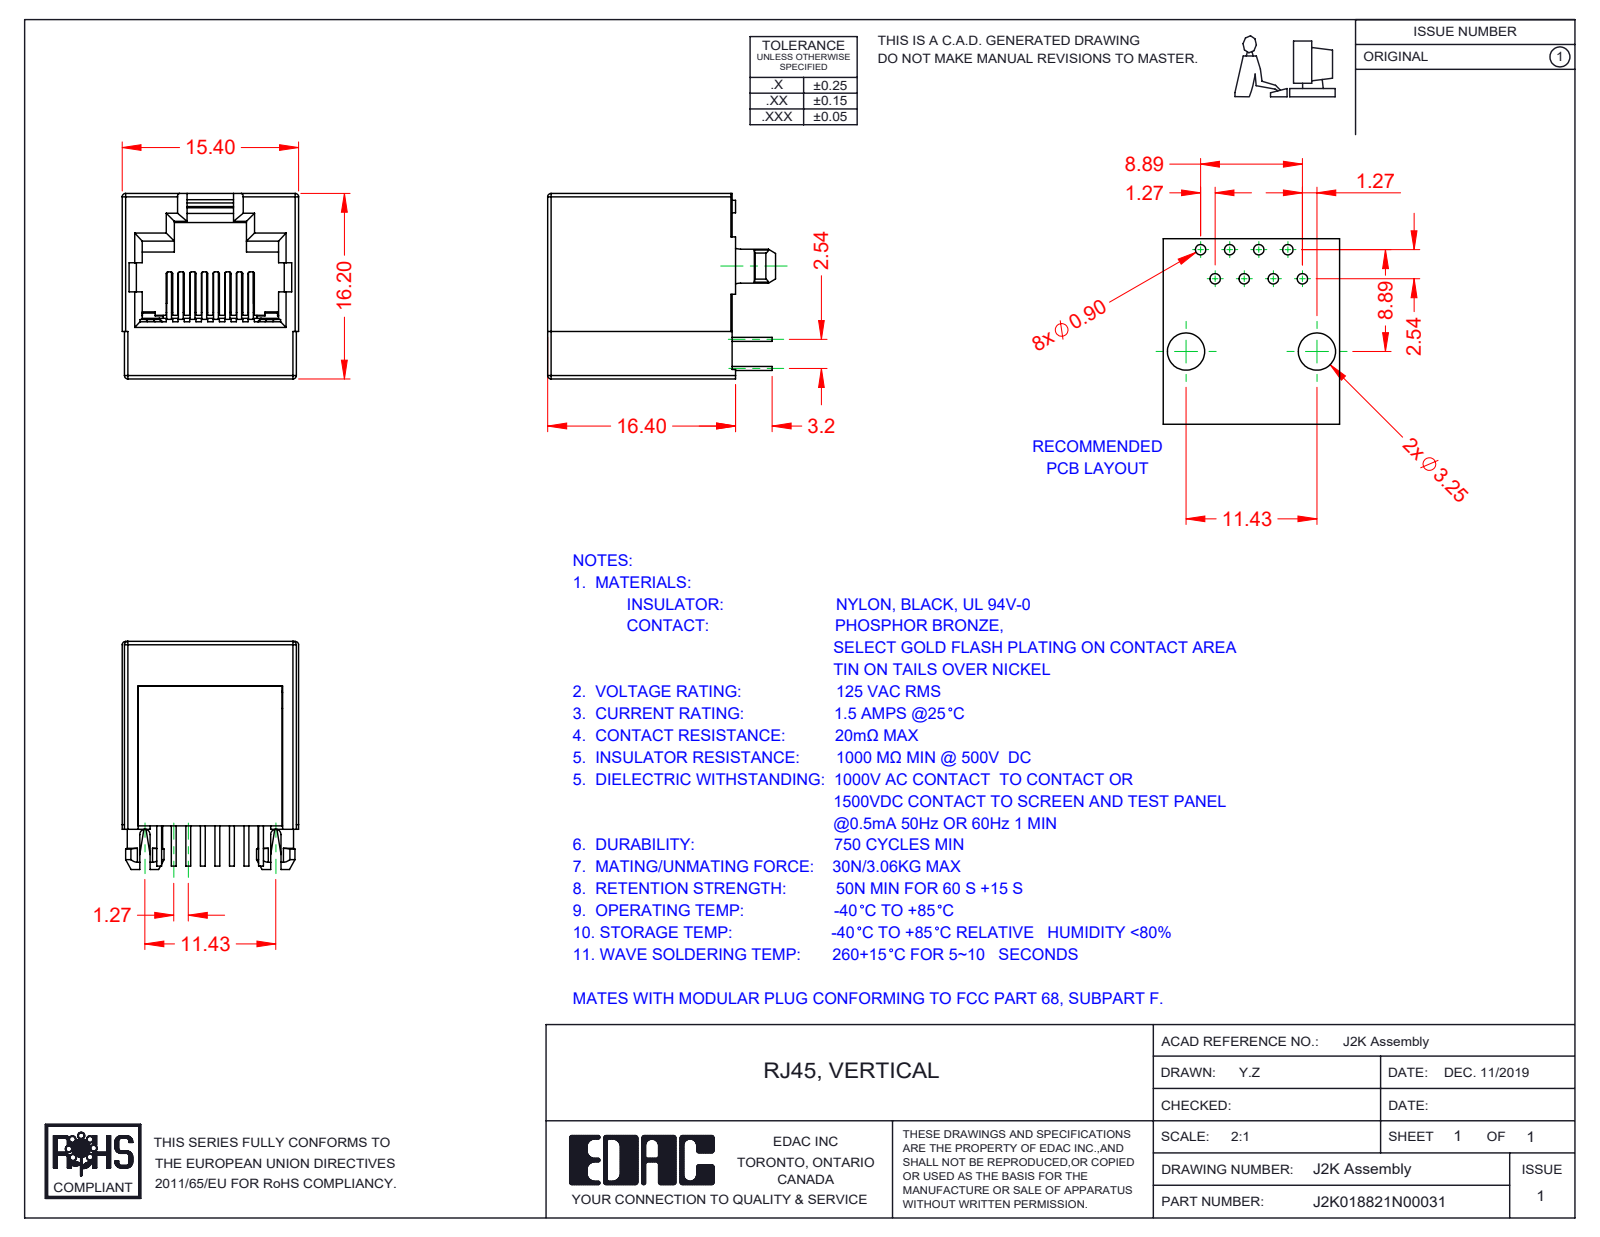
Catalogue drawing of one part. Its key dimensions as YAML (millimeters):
part_name: "2K Insulator; 2K Contact Lock; 2K Contacts; RJ2K018821N00031"
step_written_by: "SolidWorks 2016 (CONFIG_CONTROL_DESIGN)"
units: millimeters
bodies: {solids: 10, faces: 723, planar: 586, cylindrical: 113, other: 24}
overall_size: [19.9, 16.2, 15.4]
volume: 2473
surface_area: 3962
round_bosses_or_shafts:
  - {diameter: 3.1, count: 2}
  - {diameter: 1.1, count: 2}
partial_cylinders:
  - {radius: 0.15, count: 16}
  - {radius: 0.3, count: 10}
  - {radius: 0.5, count: 3}
  - {radius: 0.1, count: 2}
  - {radius: 0.2, count: 2}
  - {radius: 0.45, count: 2}
  - {radius: 0.6, count: 2}
  - {radius: 0.95, count: 2}
face_to_face_distances: [16.2, 15.4, 1.4, 14, 1.2, 13.8, 15.2, 0.35, 0.5, 15]
